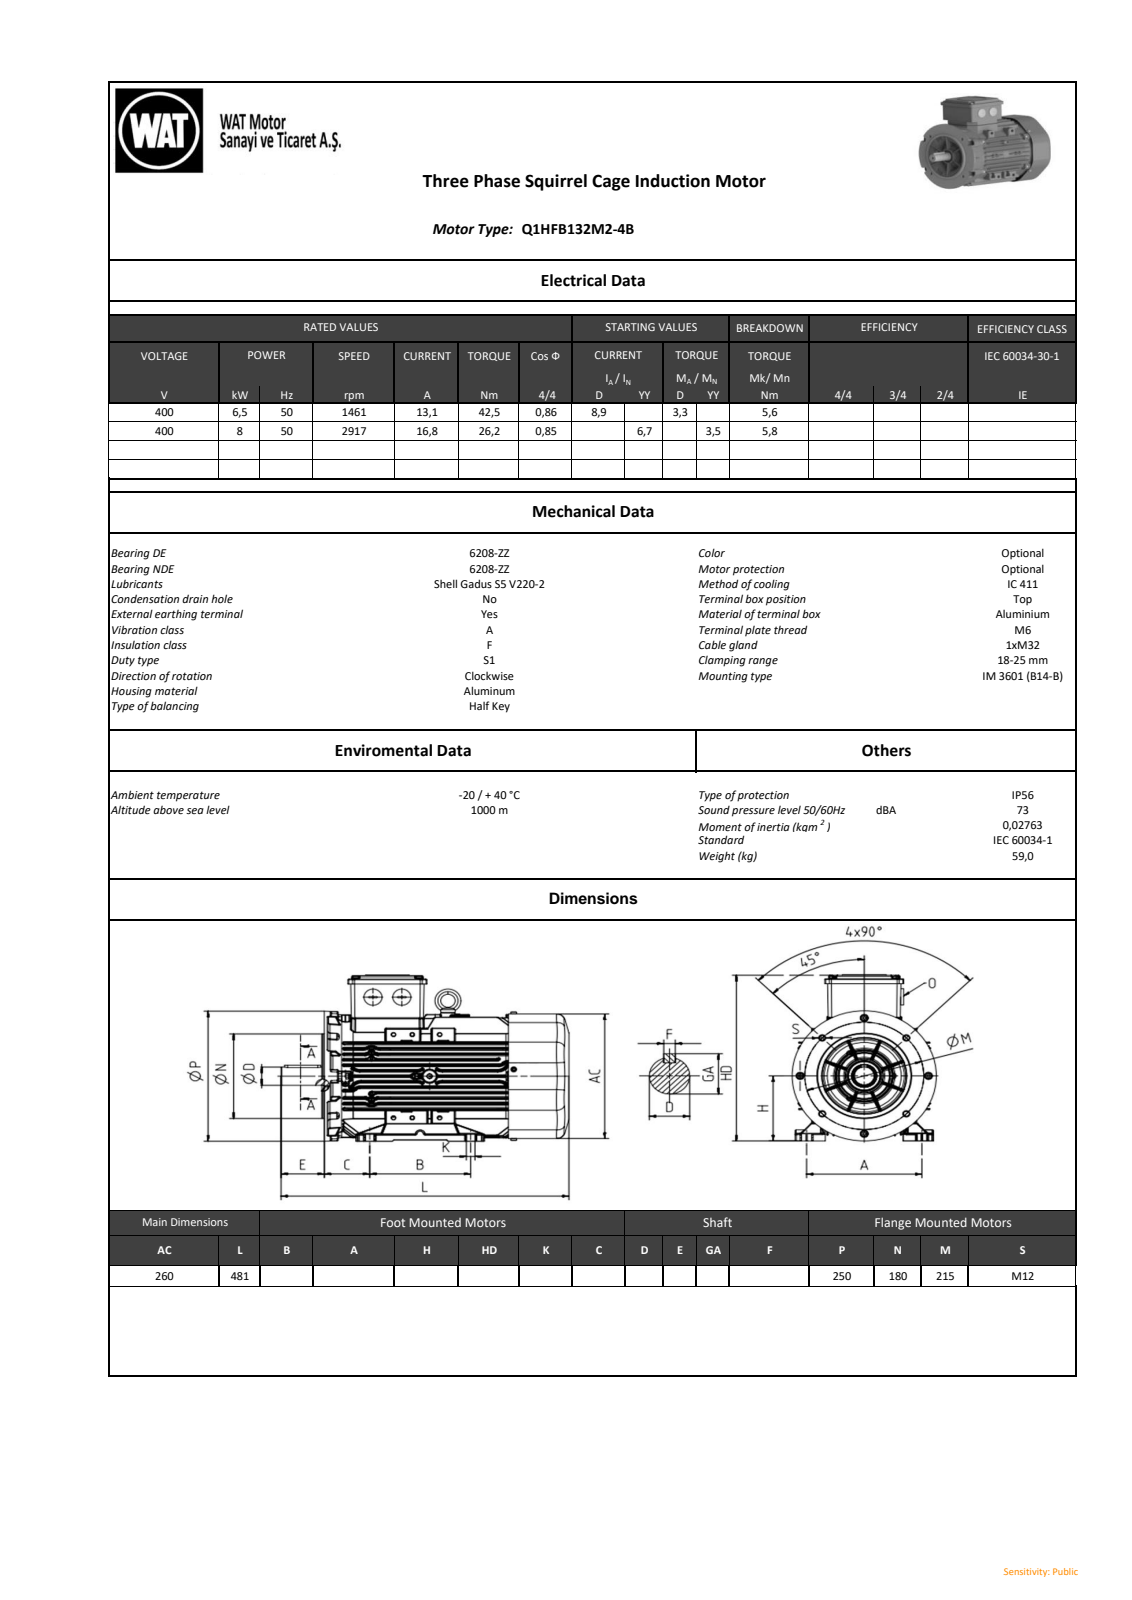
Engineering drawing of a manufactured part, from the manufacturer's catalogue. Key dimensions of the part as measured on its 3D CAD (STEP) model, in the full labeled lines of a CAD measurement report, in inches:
Part name (STEP PRODUCT): QH series_ 132_B14b_stp_objects
STEP written by: SIEMENS PLM Software NX2206.8101 (AP203_CONFIGURATION_CONTROLLED_3D_DESIGN_OF_MECHANICAL_PARTS_AND_ASSEMBLIES_MIM_LF)
Units: inches
Bodies: 0 solids, 5962 faces (1456 planar, 2635 cylindrical, 1871 other)
Overall size (bounding box): 18.917 × 12.621 × 10.241
Round holes (diameter × count): ⌀0.333 ×2, ⌀0.334 ×2, ⌀0.217 ×1, ⌀0.334 ×1, ⌀0.472 ×1, ⌀0.551 ×1, ⌀0.961 ×1, ⌀2.441 ×1, ⌀3.228 ×1, ⌀7.087 ×1
Round bosses / shafts (diameter × count): ⌀0.315 ×9, ⌀1.496 ×3, ⌀0.512 ×2, ⌀9.075 ×1, ⌀3.416 ×1, ⌀1.772 ×1, ⌀1.575 ×1, ⌀1.48 ×1
Partial cylindrical surfaces — rounded edges, fillets, slot ends (radius × count): R0.031 ×933, R0.039 ×443, R0.02 ×148, R0.118 ×72, R0.079 ×52, R0.197 ×18, R2.362 ×16, R1.102 ×12
Main face-to-face distances: 0.41, 0.416, 0.059, 0.405, 0.82, 4.944, 4.535, 4.13, 3.719, 0.409
Hole centre spacings: 2.951, 3.517, 4.921, 5.63, 5.803, 6.077, 6.14, 7.044
